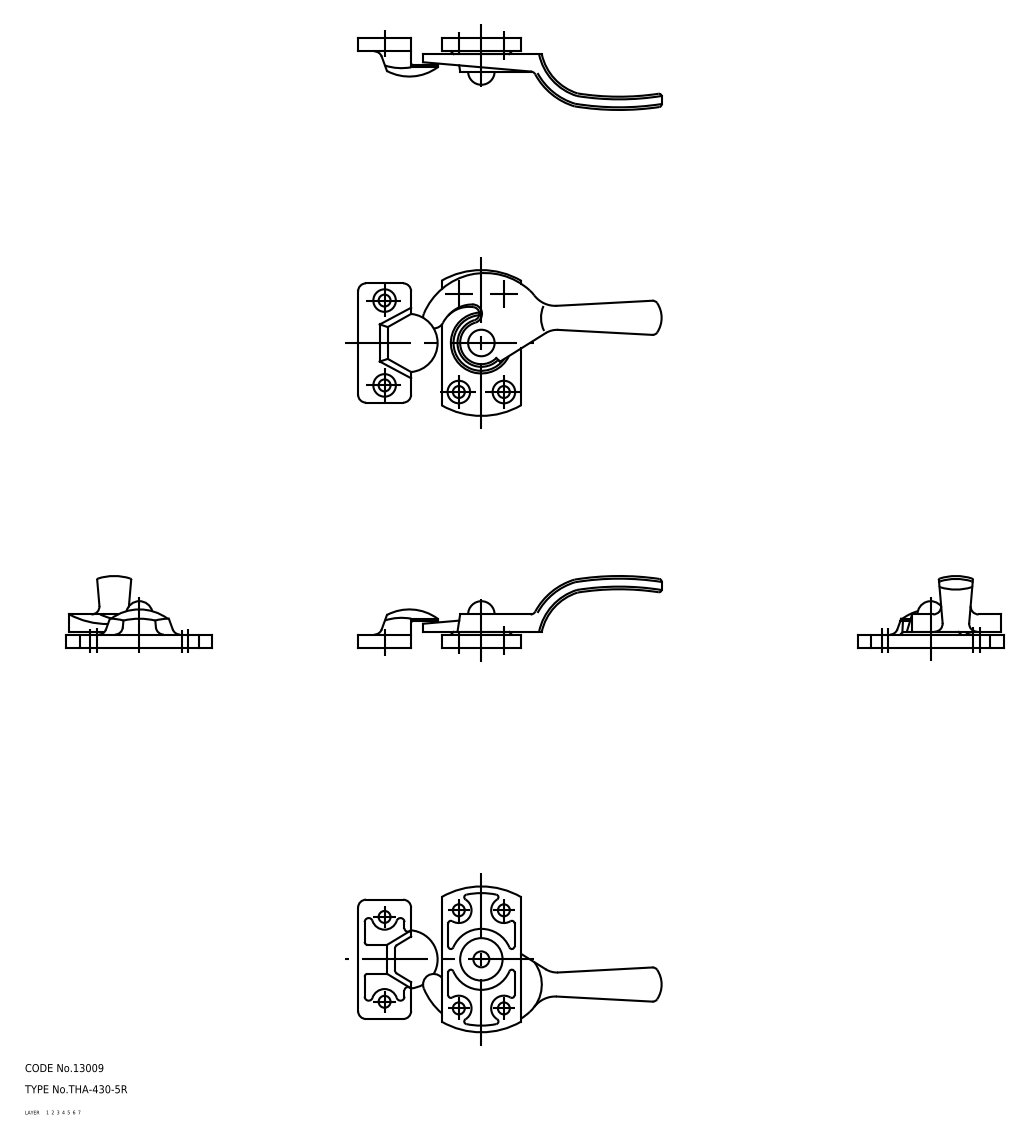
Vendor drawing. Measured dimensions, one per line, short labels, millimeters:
name: washer_C_mr; washer_B_mr; rivet_mr; keeper_mr (+3 more)
written by: CADfix (AUTOMOTIVE_DESIGN)
unit: mm
bodies: 6 solids, 166 faces (0 planar, 0 cylindrical, 166 other)
size: 114.5 × 55 × 27.1
volume: 18 875 mm³; area: 12 964 mm²
